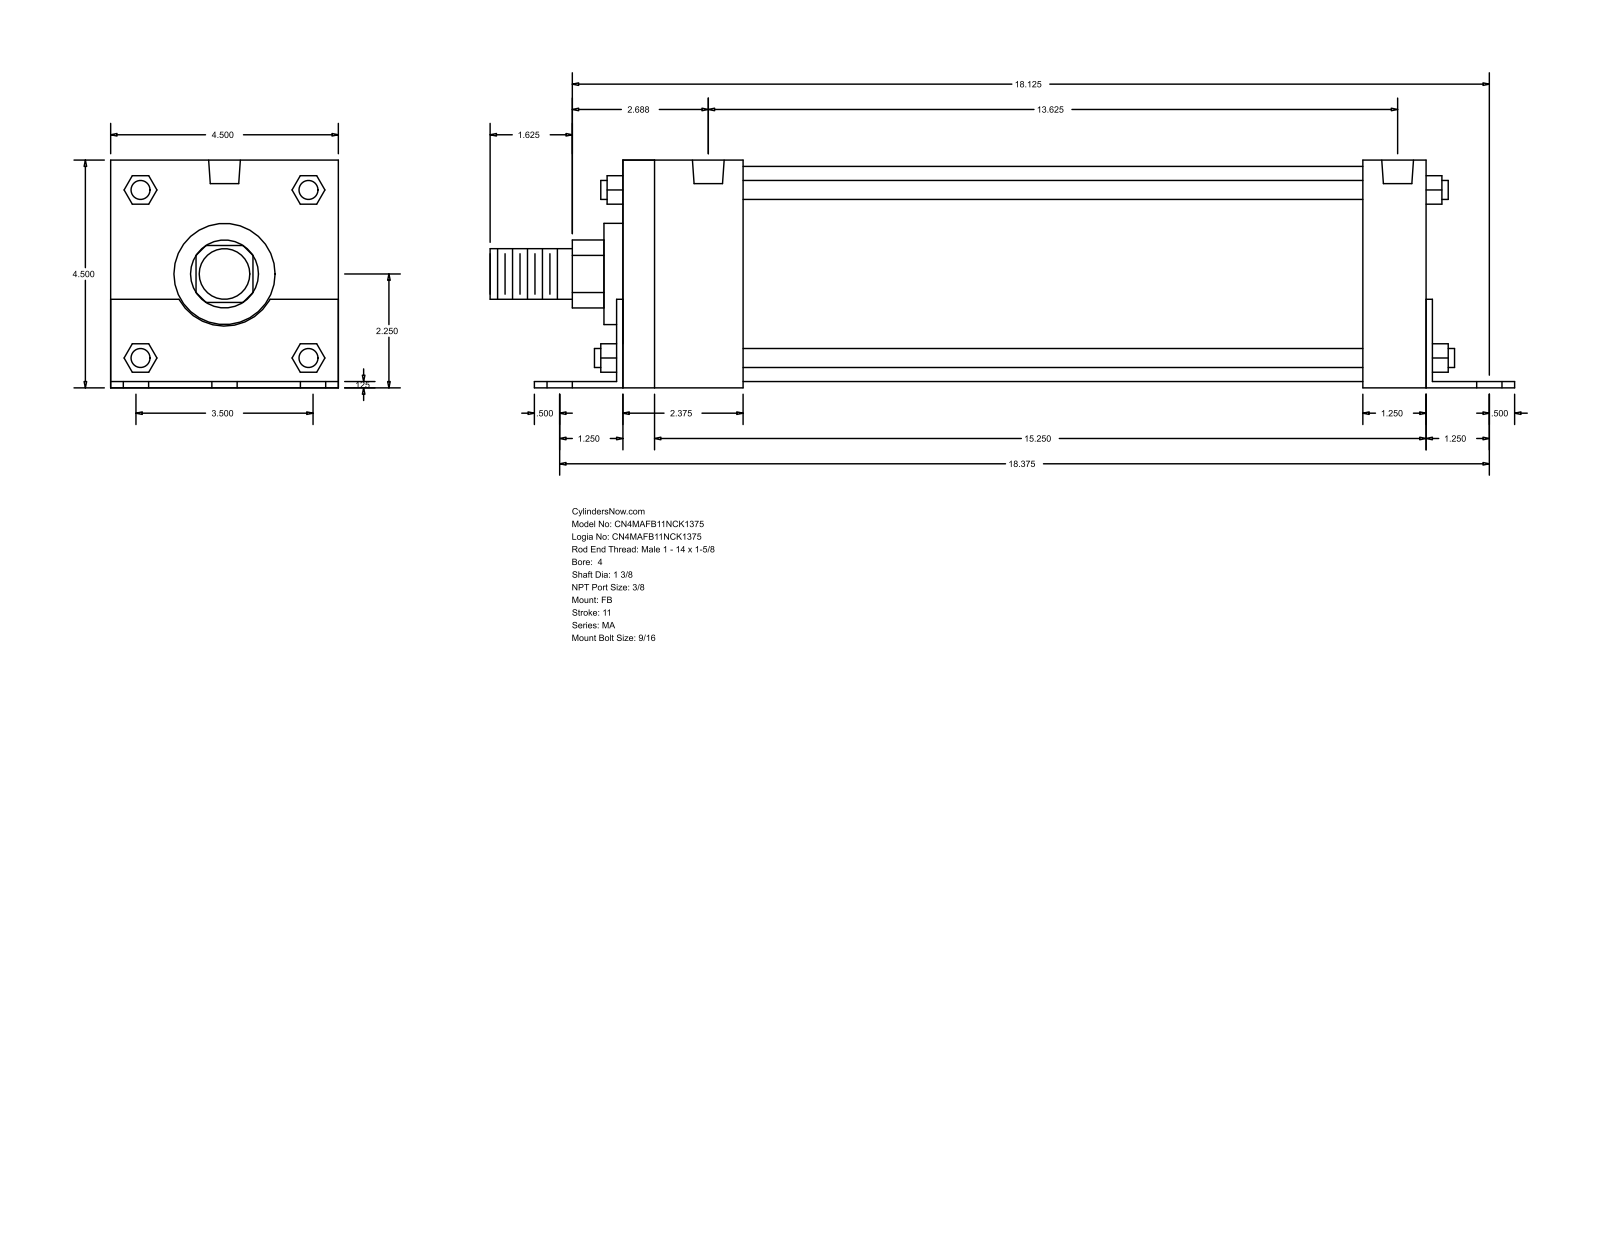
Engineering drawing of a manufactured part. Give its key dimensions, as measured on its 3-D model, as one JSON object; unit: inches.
{"part_name": "MA_FB__0400_1.375", "step_written_by": "GSSL Pune (CONFIG_CONTROL_DESIGN)", "units": "inches", "bodies": {"solids": 0, "faces": 140, "planar": 105, "cylindrical": 35, "other": 0}, "overall_size": [20.25, 4.502, 4.5], "round_holes": [[0.563, 6], [0.437, 4], [0.627, 2]], "round_bosses_or_shafts": [[0.375, 4], [4.25, 1], [2, 1], [1.375, 1], [1, 1]], "partial_cylinders_radius": [[0.672, 1], [1.03, 1]], "face_to_face_distances": [4.5, 0.125, 4.502, 0.123, 4.377, 15.875, 0.125, 16, 16, 16.125], "hole_center_spacings": [1.75, 18.458, 18.375, 0.188, 2.52, 2.658, 3.419, 3.5]}
